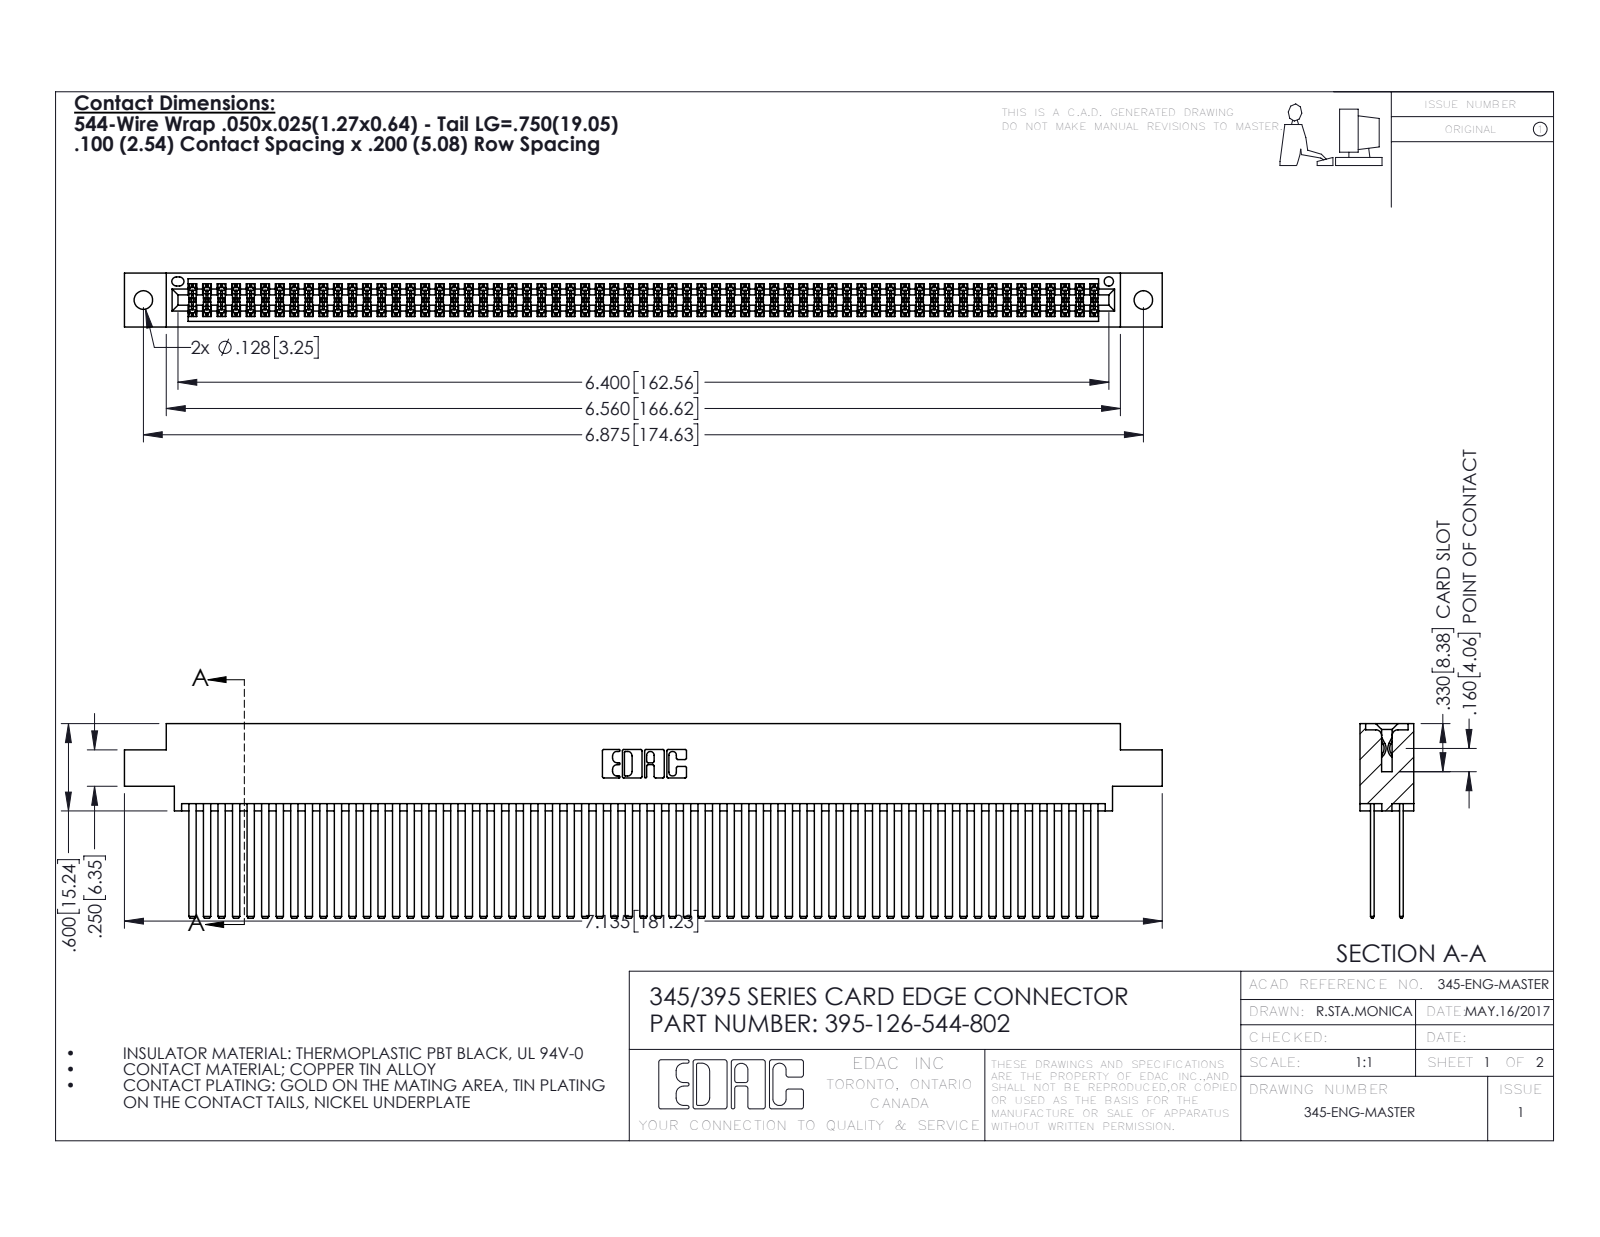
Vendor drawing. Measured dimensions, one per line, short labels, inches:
name: 395-126-544-802; 345-292-001_345-293-144; 345 Part_0.170 Offset - 0.128 Dia
written by: SolidWorks 2016 (CONFIG_CONTROL_DESIGN)
unit: in
bodies: 127 solids, 5674 faces (3738 planar, 1936 cylindrical, 0 other)
size: 7.135 × 1.337 × 0.37
volume: 1.185 in³; area: 52.94 in²
holes: 2× ⌀0.128, 1× ⌀0.064
rounds: 189× R0.006, 22× R0.01, 6× R0.007, 6× R0.031, 3× R0.026, 2× R0.014, 2× R0.019, 2× R0.022
face distances: 0.2, 0.025, 0.298, 0.072, 0.098, 0.272, 0.225, 0.175, 0.37, 0.15
hole spacings: 0.27, 6.639, 6.875
